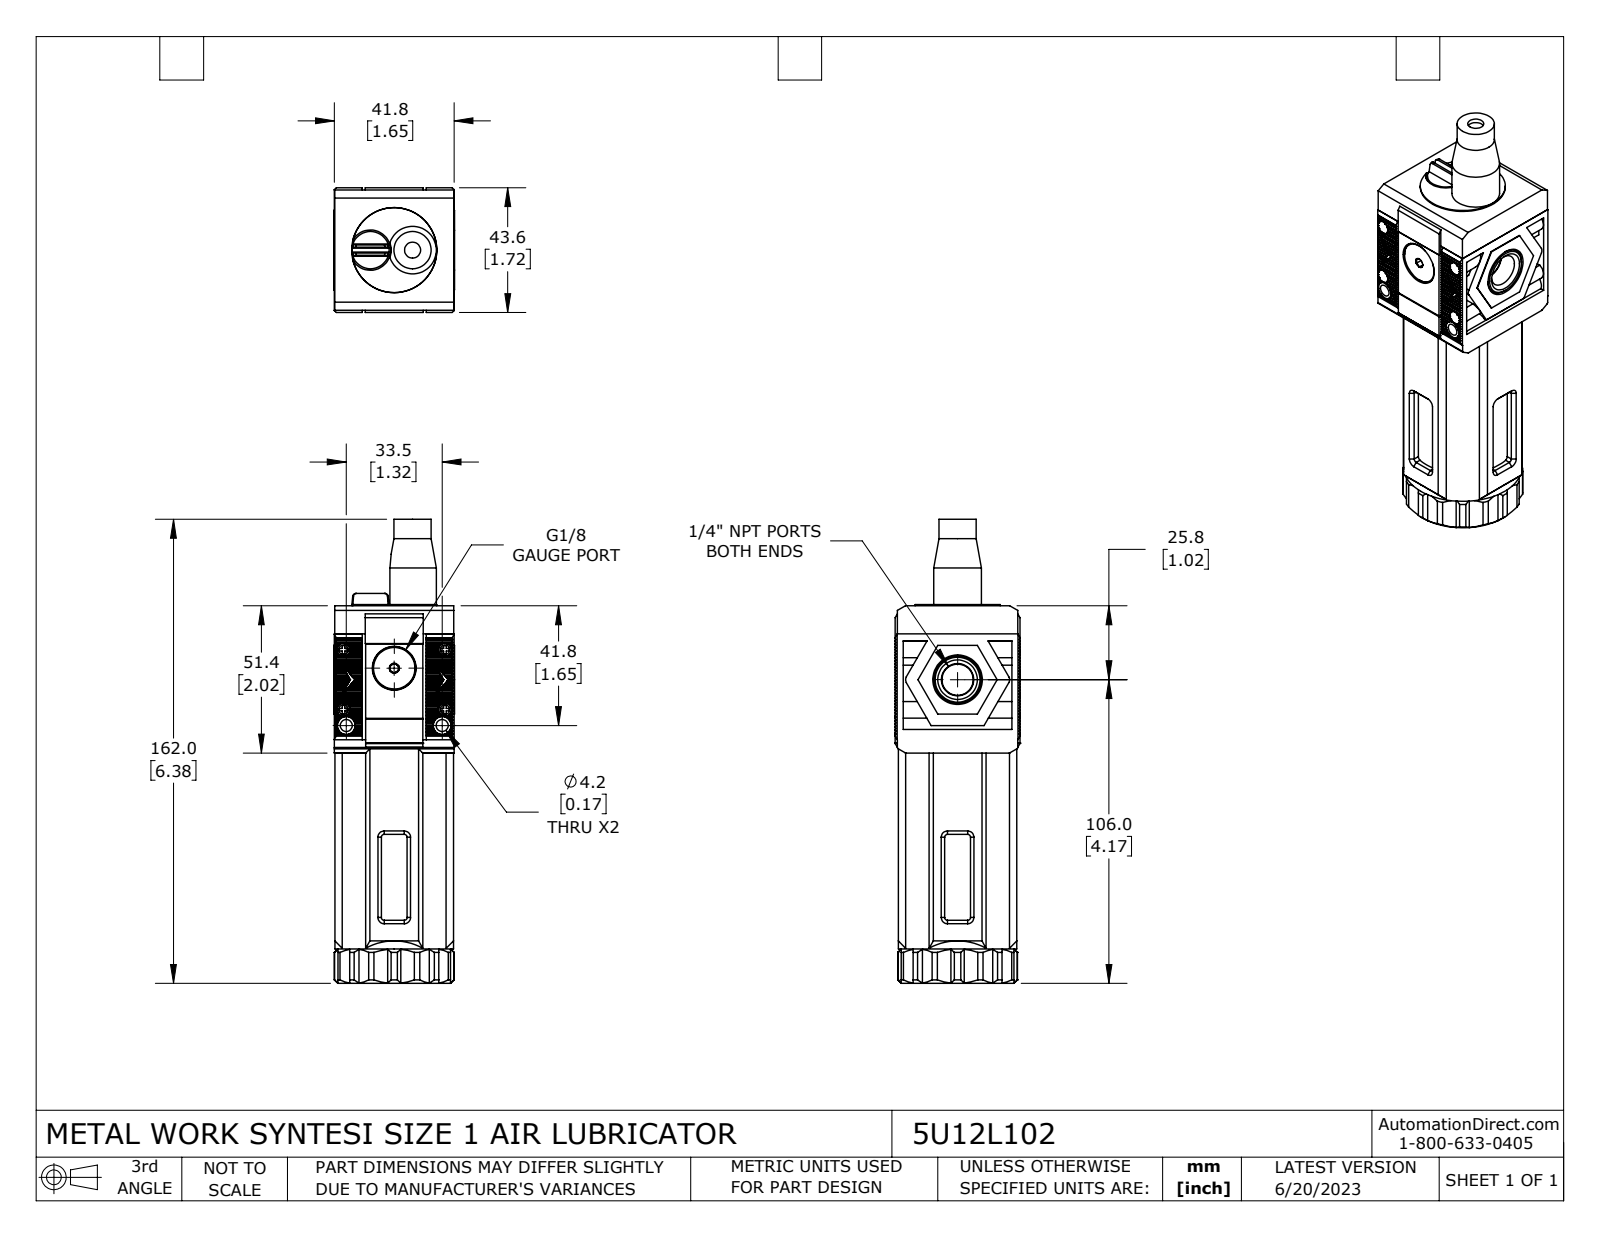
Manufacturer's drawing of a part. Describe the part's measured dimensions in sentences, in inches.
The part is named "5U12L102". Its 3-D file was written by "SolidWorks 2021 (CONFIG_CONTROL_DESIGN)". It is 14 solids with 1343 faces: 921 planar, 262 cylindrical and 160 other. Overall it measures 6.378 by 1.717 by 1.661 inches. Its volume is 8.25 cubic inches and its surface area 101.5 square inches. Round holes: 4 of diameter 0.083, 4 of diameter 0.118, 4 of diameter 0.185, 2 of diameter 0.165, 1 of diameter 0.22, 1 of diameter 0.337, 1 of diameter 0.555, 1 of diameter 0.602, 1 of diameter 1.169, 1 of diameter 1.181, 1 of diameter 1.232, 1 of diameter 1.339. Round bosses or shafts: 4 of diameter 0.181, 4 of diameter 0.102, 2 of diameter 0.512, 2 of diameter 0.244, 1 of diameter 1.63, 1 of diameter 1.402, 1 of diameter 0.984, 1 of diameter 0.898. Partial cylindrical surfaces (rounded edges, fillets, slot ends): 8 of radius 0.039, 4 of radius 0.024, 4 of radius 0.122, 2 of radius 0.008, 2 of radius 0.079, 1 of radius 0.285, 1 of radius 0.433, 1 of radius 0.823. The main face-to-face distances are 1.638, 1.63, 0.043, 1.673, 0.299, 1.646, 1.331, 1.575, 1.339, 1.642. The hole center spacings are 0.222, 0.742, 0.823, 0.9, 1.027, 1.042, 1.374, 1.394.
